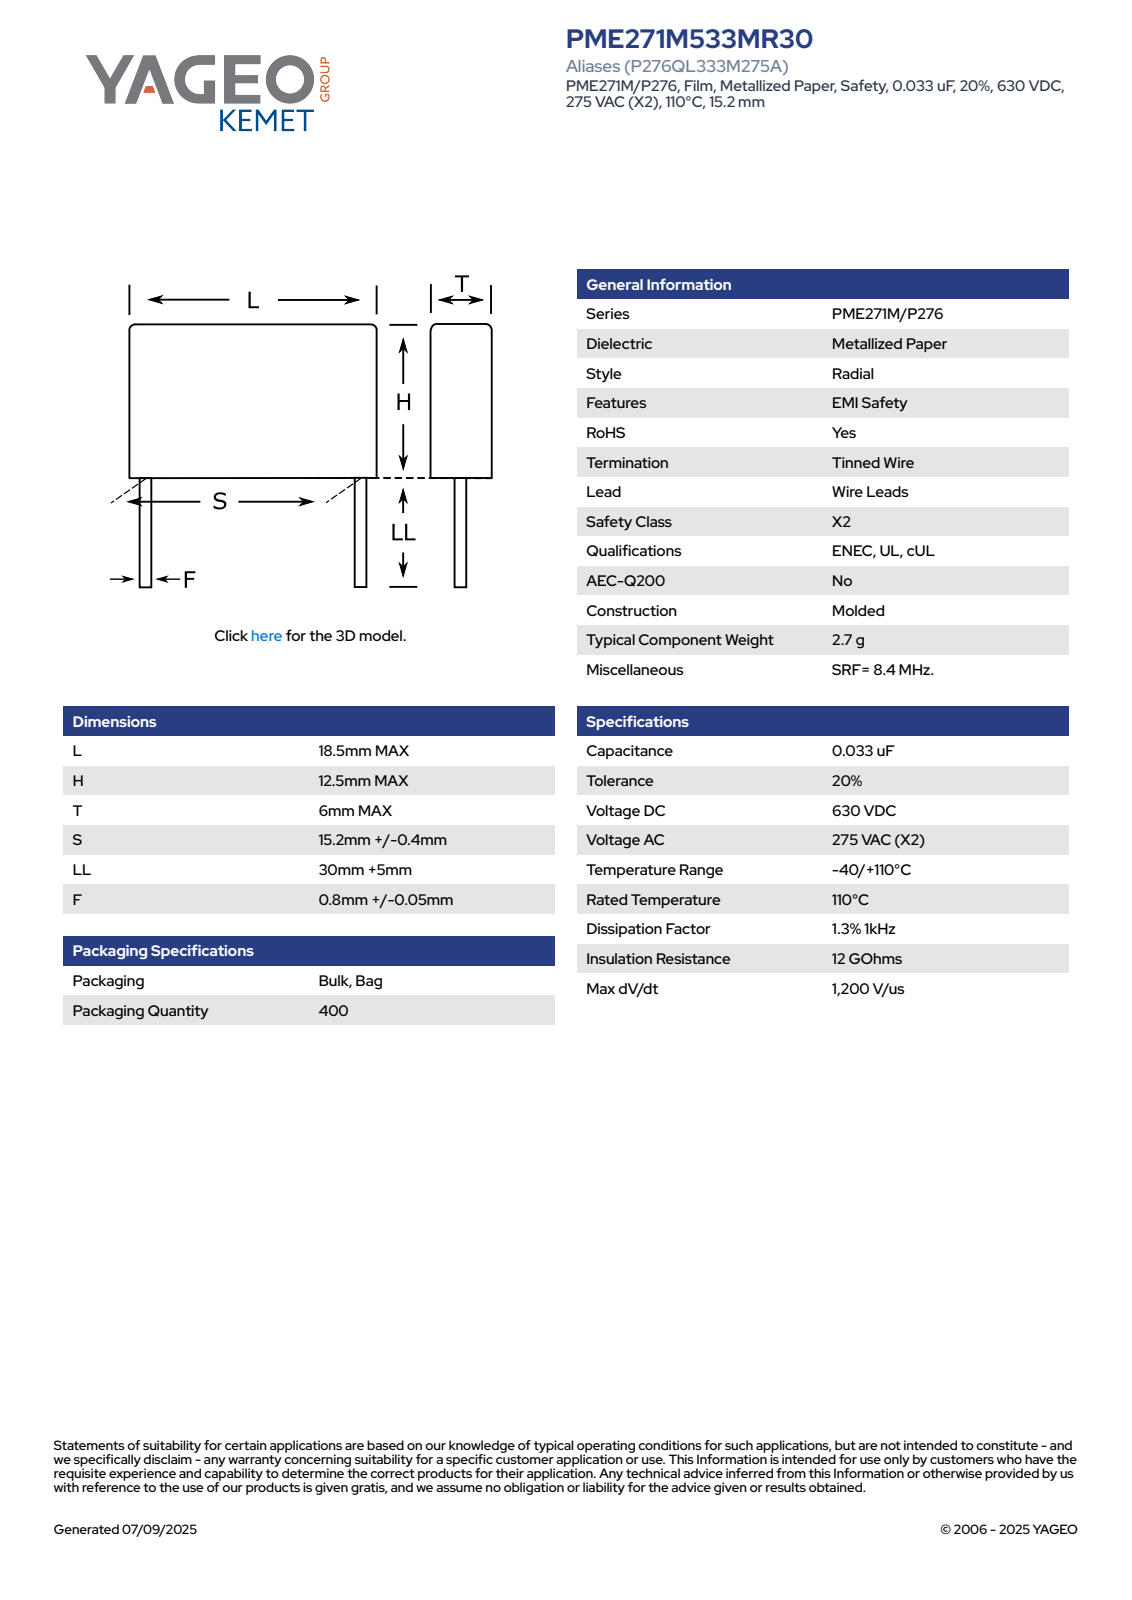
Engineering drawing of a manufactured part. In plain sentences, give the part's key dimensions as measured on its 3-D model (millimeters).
The part is named "CFR_MOLDED_18.5X12.5X6_L18.5H12.5T6S15.2LL35F0.8". Its 3-D file was written by "SolidWorks 2014 (AUTOMOTIVE_DESIGN)". It is 4 solids with 73 faces: 65 planar, 8 cylindrical and 0 other. Overall it measures 47.5 by 18.5 by 6 millimeters. Its volume is 1 420 cubic millimeters and its surface area 1 016 square millimeters. Round bosses or shafts: 2 of diameter 0.8. Partial cylindrical surfaces (rounded edges, fillets, slot ends): 4 of radius 0.5. The main face-to-face distances are 6, 12.5, 18.5, 35, 47.5, 41.9, 6.9, 5.6, 40.24, 5.24.
